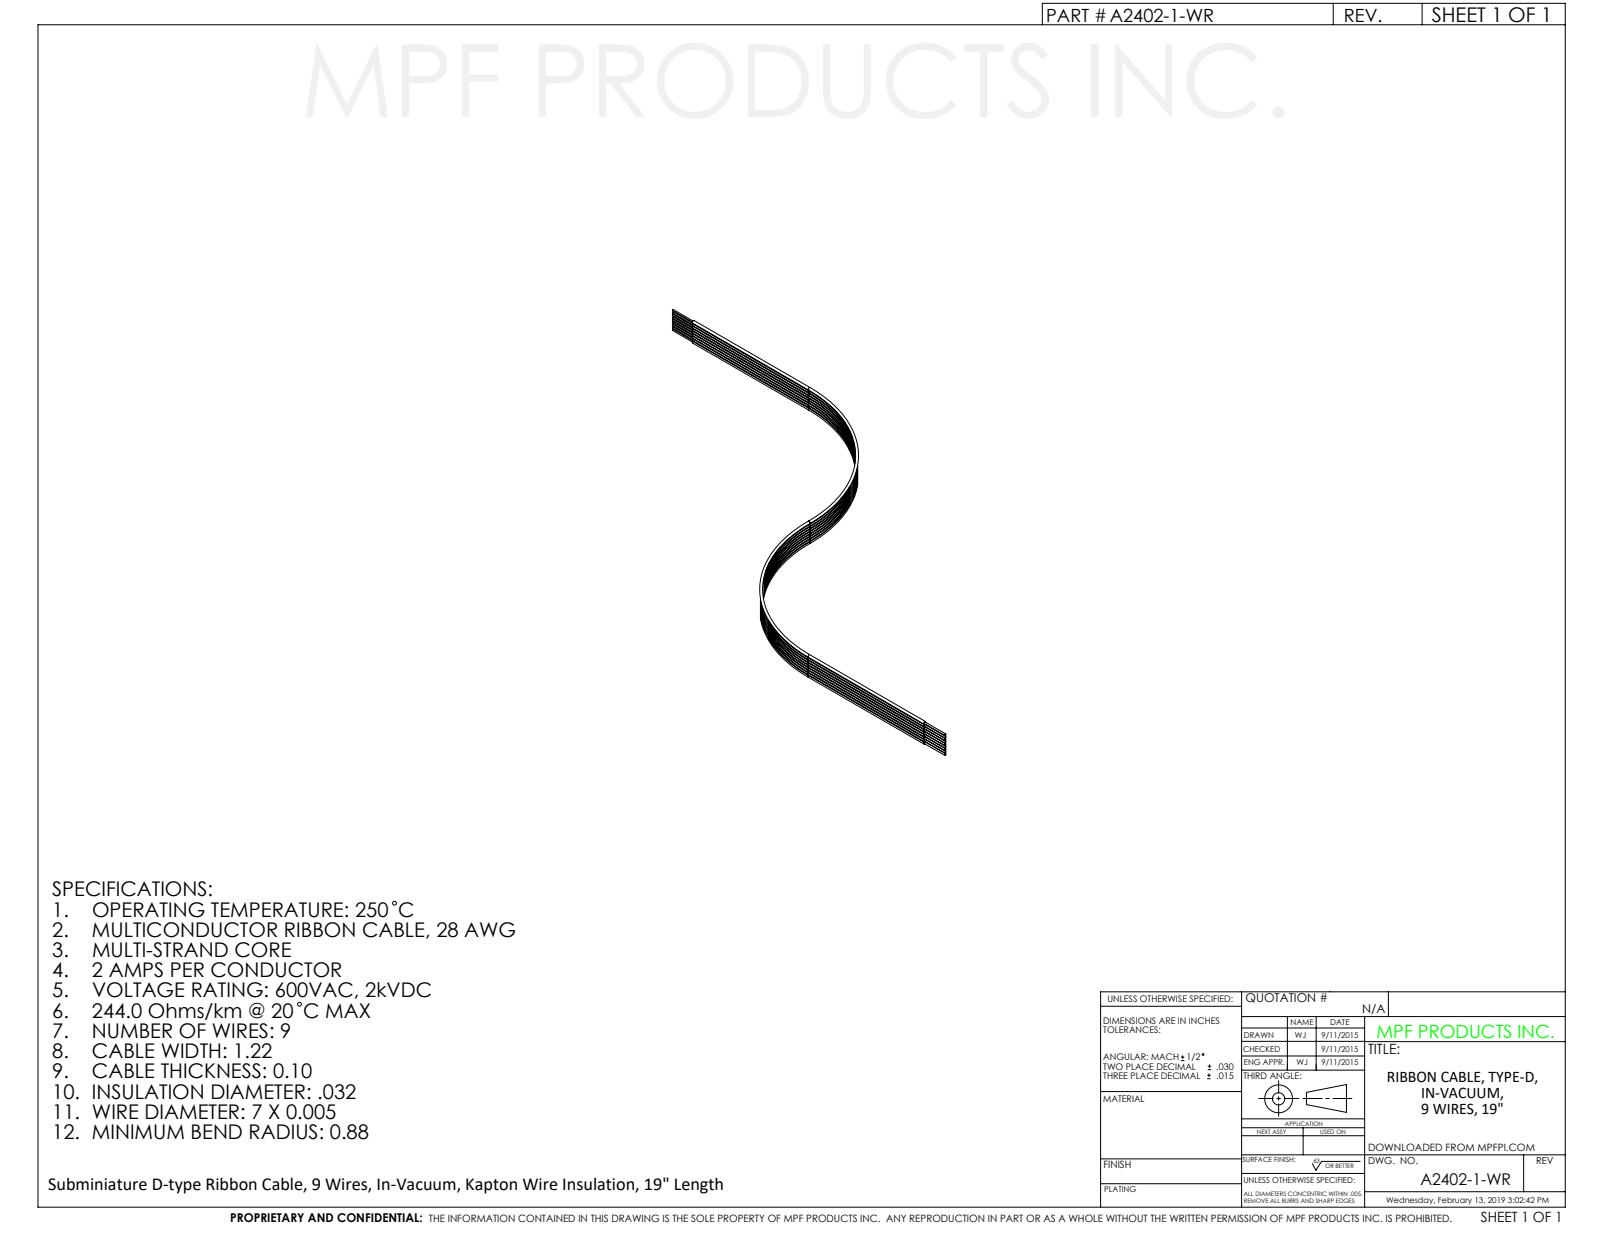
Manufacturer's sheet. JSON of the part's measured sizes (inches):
{"part_name": "A2402-3-WR", "step_written_by": "SolidWorks 2012 (CONFIG_CONTROL_DESIGN)", "units": "inches", "bodies": {"solids": 1, "faces": 241, "planar": 68, "cylindrical": 119, "other": 54}, "overall_size": [4.9, 2.27, 0.188], "volume_in3": 0.018, "surface_area_in2": 2.612, "round_bosses_or_shafts": [[0.012, 9], [0.009, 9]], "partial_cylinders_radius": [[0.01, 27], [1.117, 2], [1.131, 2]], "face_to_face_distances": [0.013, 2.25, 2.263, 2.237, 4.5, 0.2, 4.7, 4.9, 2.443, 2.457]}
